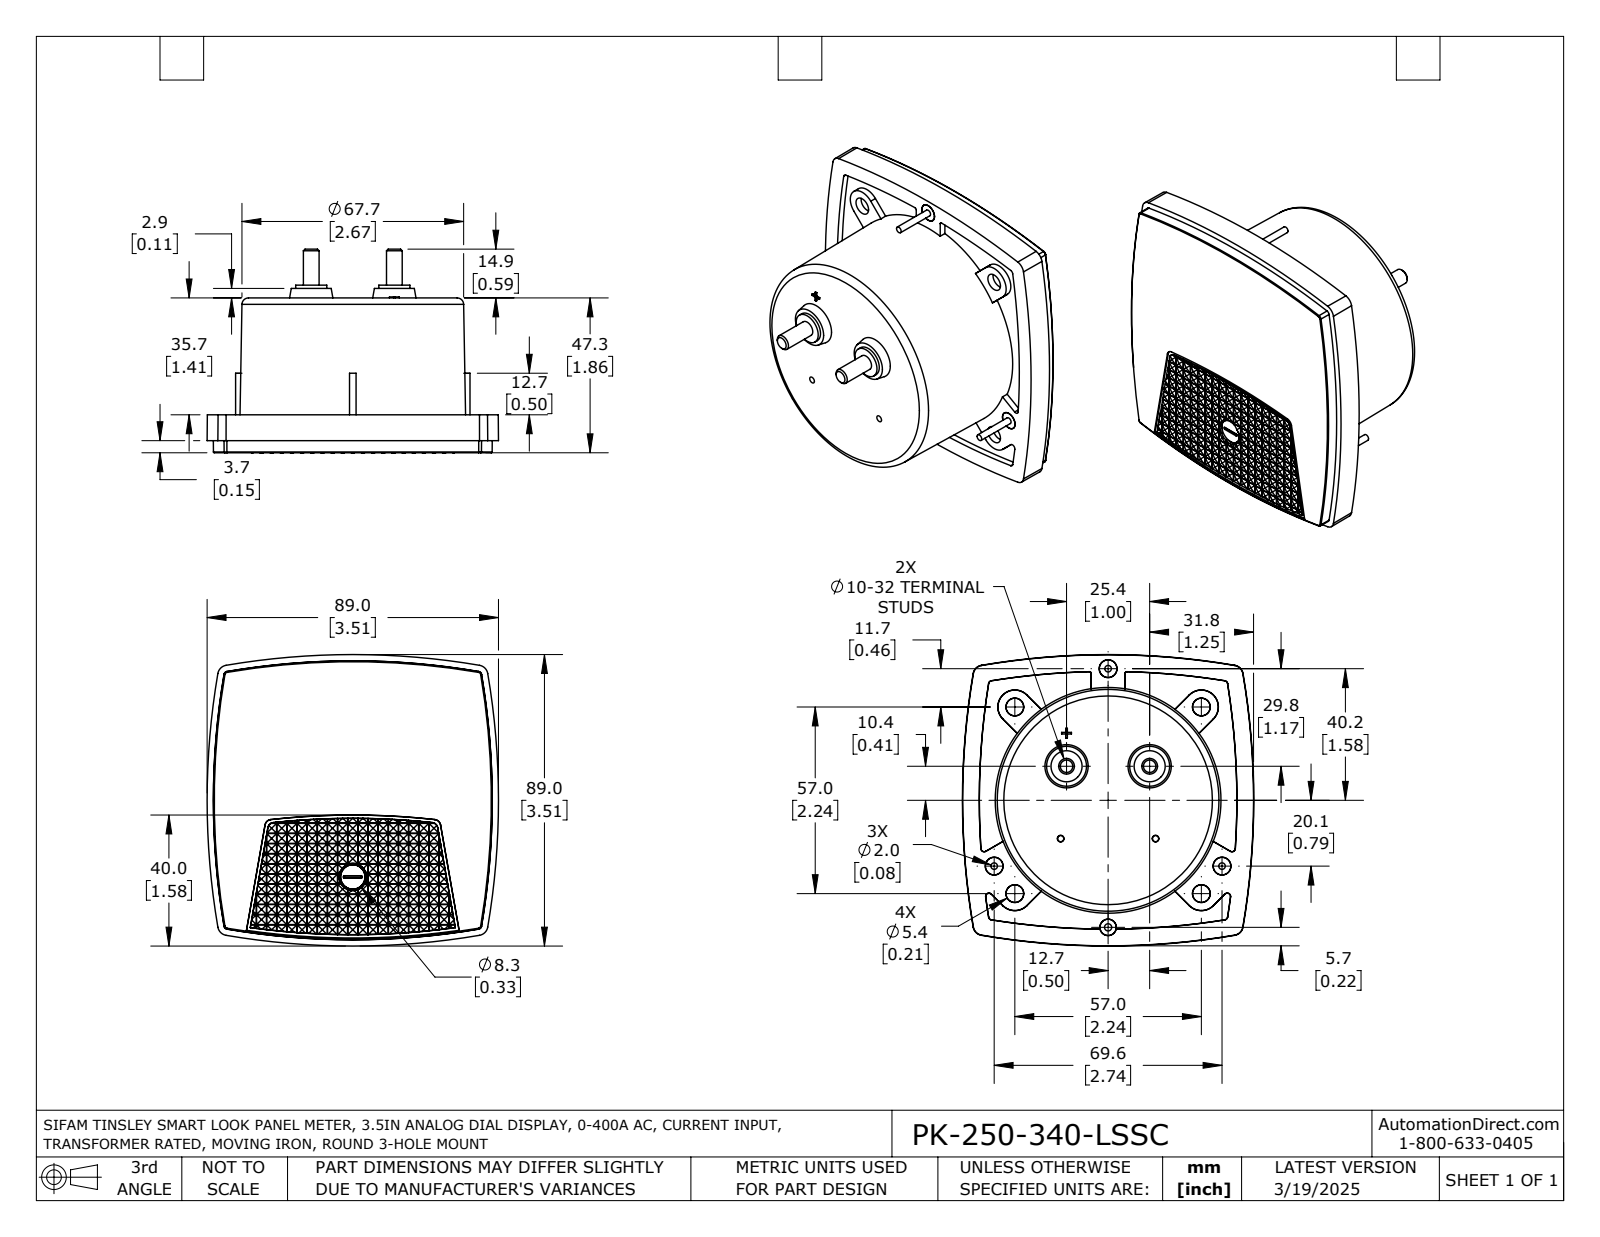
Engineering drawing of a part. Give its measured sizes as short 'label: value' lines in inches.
name: PK-250-340-LSSC
written by: SolidWorks 2021 (AUTOMOTIVE_DESIGN)
unit: in
bodies: 1 solid, 1078 faces (950 planar, 23 cylindrical, 105 other)
size: 3.505 × 3.505 × 2.453
volume: 12.99 in³; area: 44.29 in²
holes: 1× ⌀0.087
bosses: 3× ⌀0.213, 3× ⌀0.079, 2× ⌀0.374, 2× ⌀0.189
rounds: 1× R8.961
face distances: 1.862, 1.406, 0.457, 0.079, 1.484, 0.378, 0.024, 0.096, 0.072, 0.12
